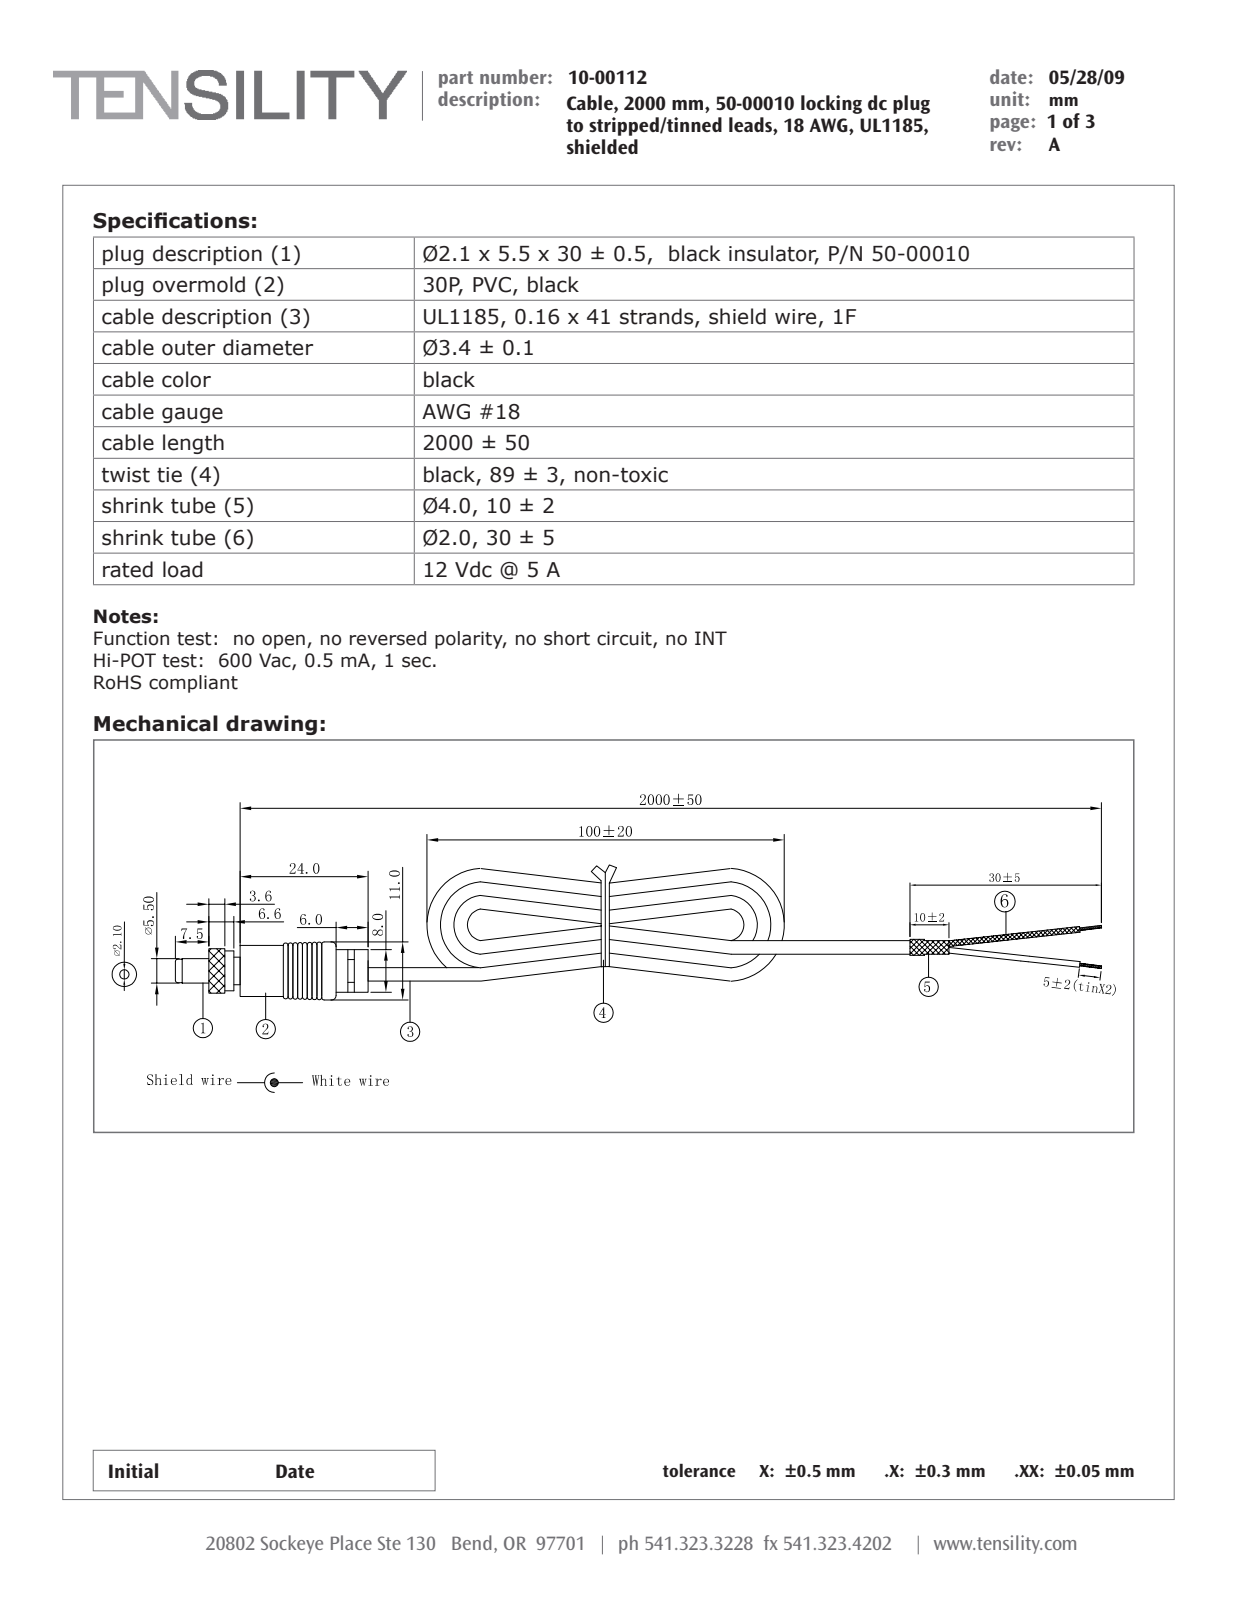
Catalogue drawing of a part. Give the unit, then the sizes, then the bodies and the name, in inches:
Units: inches
Overall size (bounding box): 8.299 × 0.433 × 0.433
Round holes (diameter × count): ⌀0.063 ×1, ⌀0.083 ×1, ⌀0.085 ×1, ⌀0.094 ×1, ⌀0.102 ×1, ⌀0.112 ×1, ⌀0.152 ×1, ⌀0.198 ×1, ⌀0.214 ×1, ⌀0.217 ×1, ⌀0.222 ×1, ⌀0.252 ×1
Round bosses / shafts (diameter × count): ⌀0.433 ×1, ⌀0.394 ×1, ⌀0.315 ×1, ⌀0.276 ×1, ⌀0.244 ×1, ⌀0.236 ×1, ⌀0.216 ×1, ⌀0.209 ×1
Partial cylindrical surfaces — rounded edges, fillets, slot ends (radius × count): R0.008 ×8, R0.03 ×2, R0.154 ×1
Main face-to-face distances: 0.059, 0.945, 1.276, 0.528, 0.843, 0.331, 0.102, 1.114, 0.783, 0.161
Volume: 0.203 in³ · Surface area: 11.31 in²
Bodies: 93 solids, 2145 faces (805 planar, 474 cylindrical, 866 other)
Part name (STEP PRODUCT): 10-00112; 50-00010 interior shell; 24-00016; 50-00010 (+6 more)
STEP written by: SolidWorks 2015 (CONFIG_CONTROL_DESIGN)
